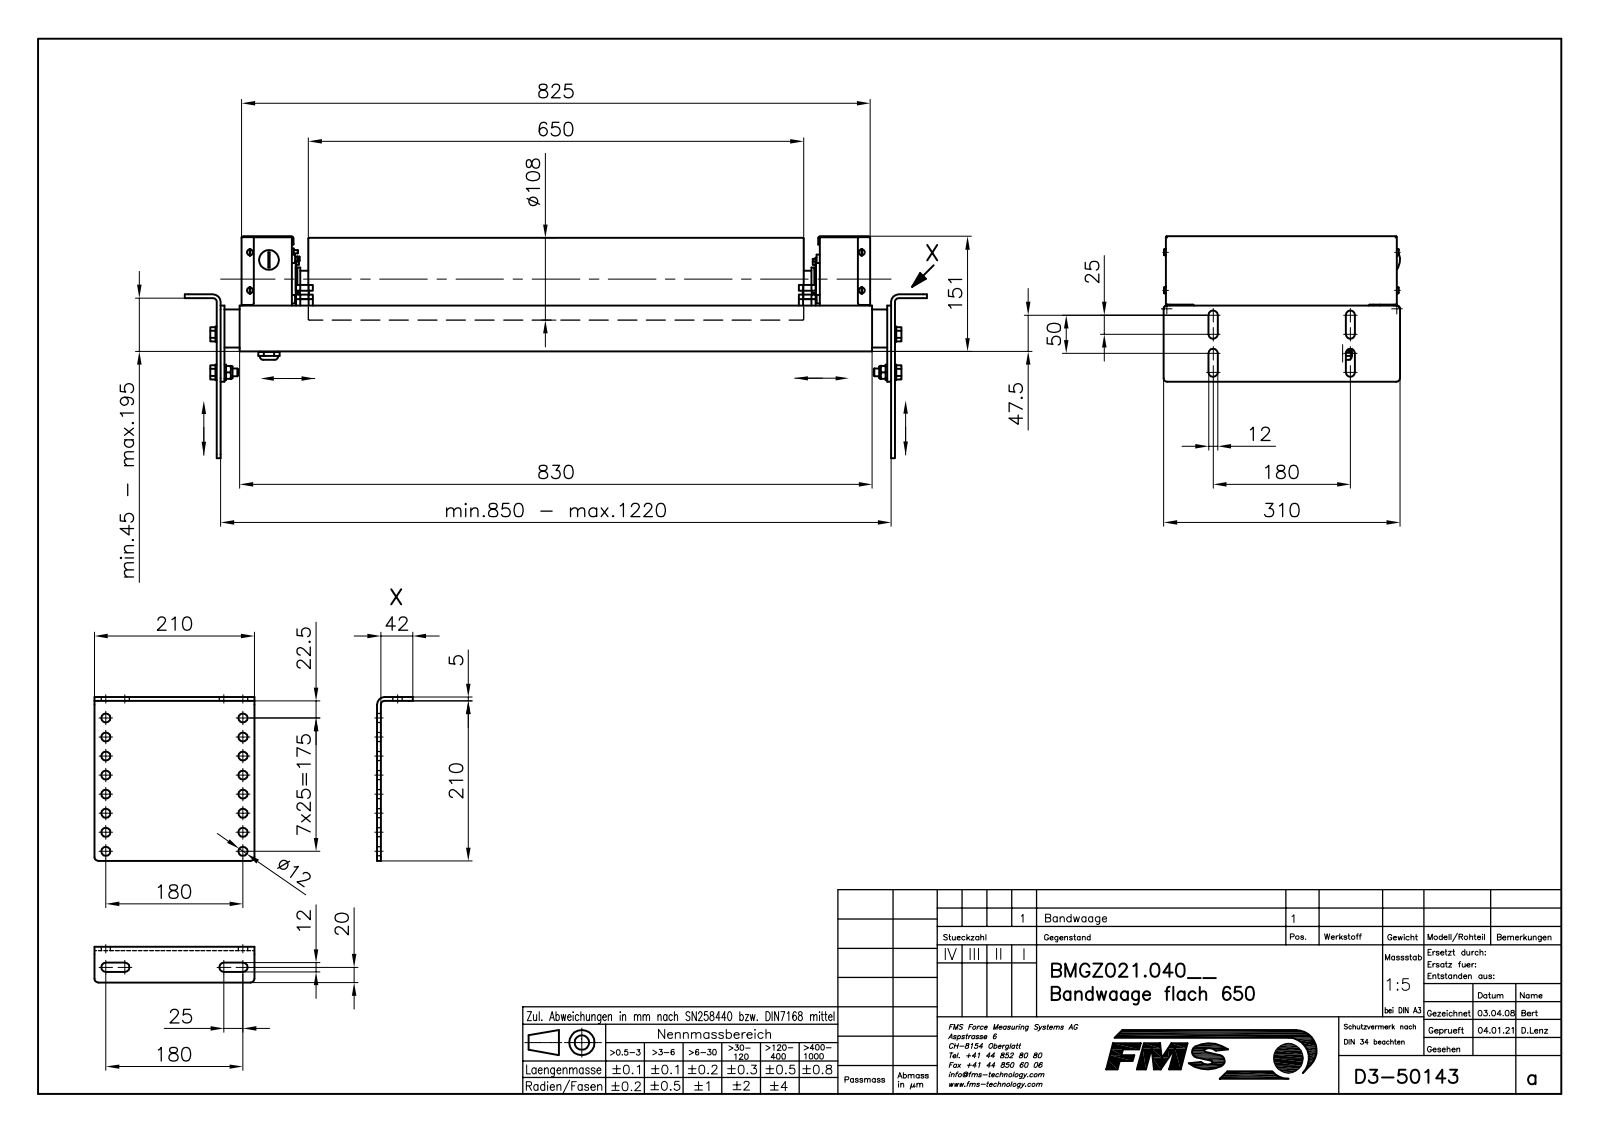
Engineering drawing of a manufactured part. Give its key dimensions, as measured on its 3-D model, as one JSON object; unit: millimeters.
{"part_name": "B50143_STP; B50105; 6KT-SCHRAUBE_M12X30; ZYL_SCHR__M4X8 (+8 more)", "step_written_by": "Mechanical Desktop 2009 (CONFIG_CONTROL_DESIGN)", "units": "millimeters", "bodies": {"solids": 136, "faces": 2360, "planar": 1273, "cylindrical": 820, "other": 267}, "overall_size": [1381.77, 310.2, 291], "volume_mm3": 9499000, "surface_area_mm2": 2284000, "round_holes": [[12, 17], [5, 6], [3.5, 4], [4.9, 4], [6.4, 4], [8.68, 4], [8.75, 4], [10, 4], [10.5, 4], [10.68, 4], [14.8, 4], [6, 3]], "round_bosses_or_shafts": [[12, 11], [8.2, 8], [4.2, 8], [20, 6], [10, 6], [5, 5], [16, 4], [11.1, 4]], "partial_cylinders_radius": [[2, 34], [1, 24], [4, 16], [5, 16], [6, 12], [3.5, 8], [2.25, 6], [0.5, 4]], "face_to_face_distances": [4, 5, 1, 36, 270, 3, 880, 27.5, 10, 266], "hole_center_spacings": [25, 50, 181.73, 186.82, 75, 195, 100, 180]}
